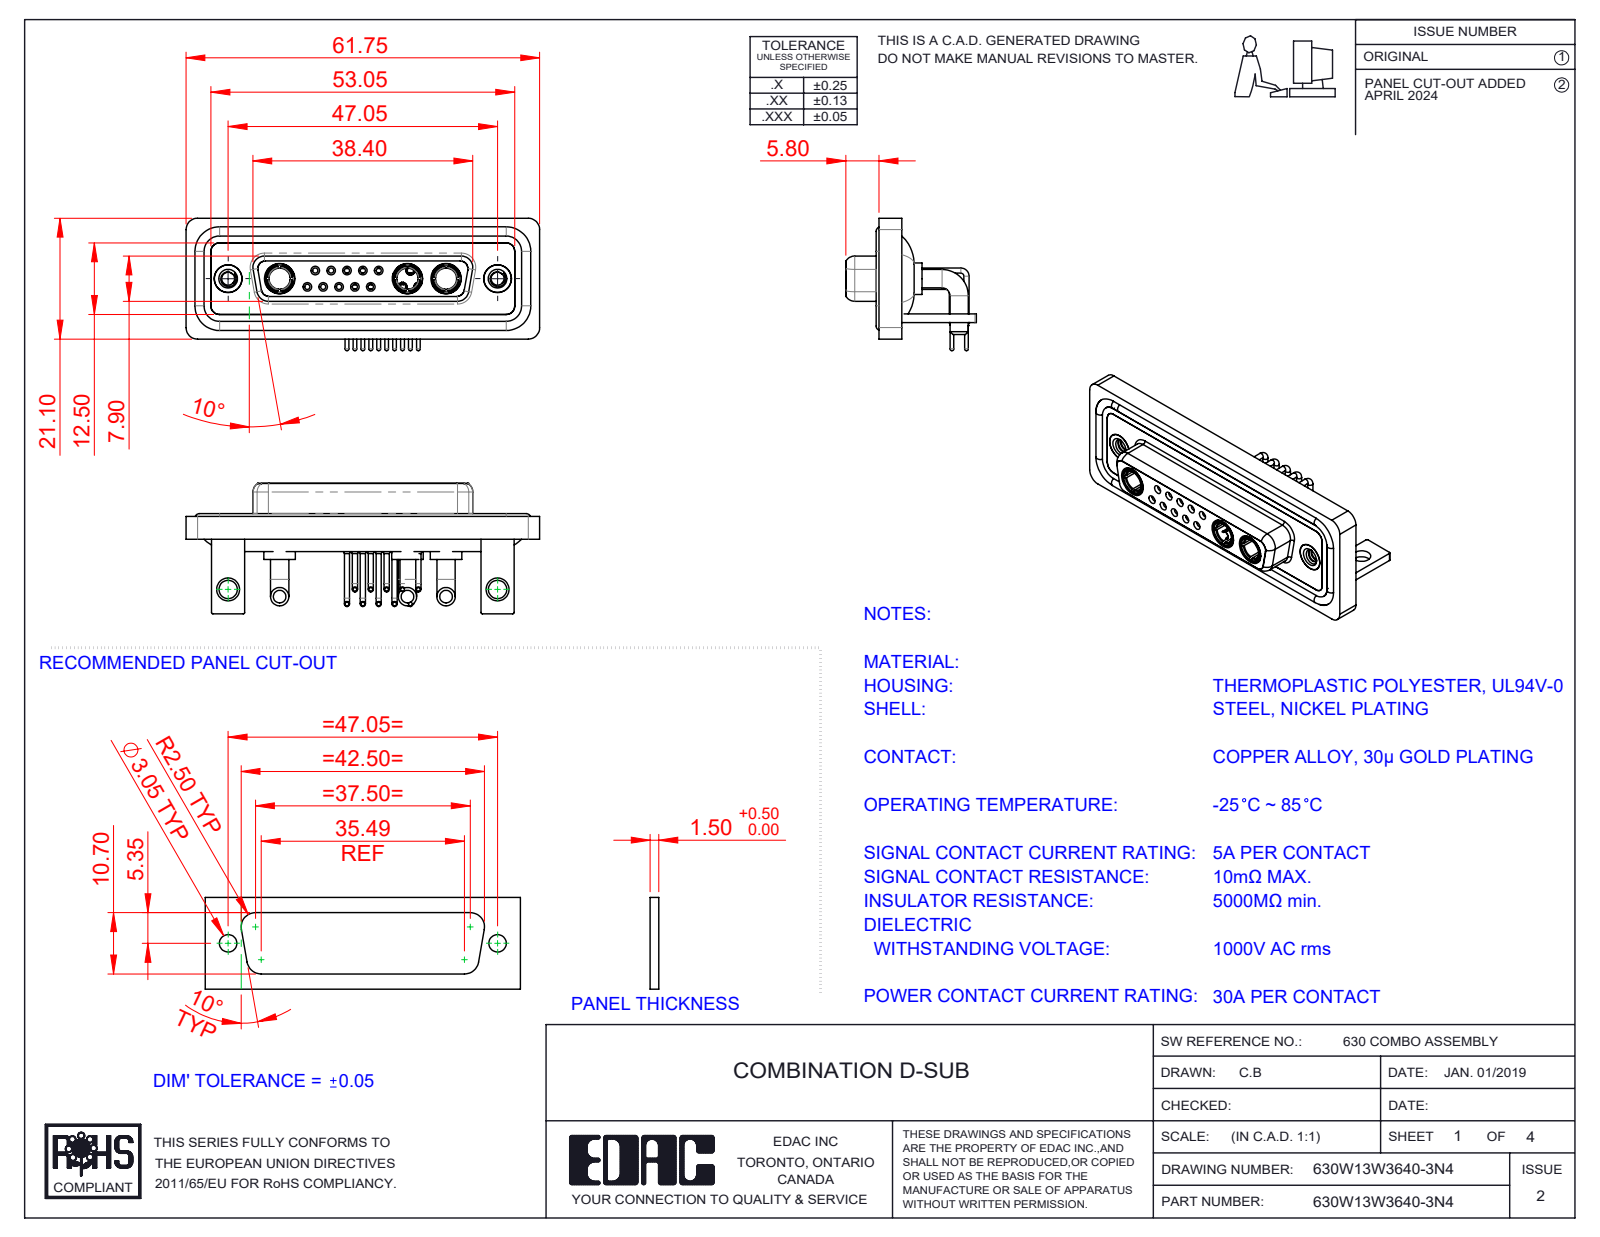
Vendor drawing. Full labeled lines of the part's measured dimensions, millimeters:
Part name (STEP PRODUCT): Power Socket_30A RA; 630Combo Threaded Rivet_2; 630Combo Stabilizer Bracket_50 Contacts; 630Combo Contact Row 1_50 Contacts (+6 more)
STEP written by: SolidWorks 2023 (CONFIG_CONTROL_DESIGN)
Units: millimetres
Bodies: 25 solids, 1198 faces (362 planar, 517 cylindrical, 319 other)
Overall size (bounding box): 61.75 × 23.12 × 22.8
Volume: 8 921 mm³ · Surface area: 15 087 mm²
Round holes (diameter × count): ⌀0.9 ×10, ⌀1.1 ×10, ⌀1.5 ×10, ⌀2 ×10, ⌀1.6 ×5, ⌀1.7 ×5, ⌀4.85 ×5, ⌀3.7 ×3, ⌀5.3 ×3, ⌀2.26 ×2, ⌀3.2 ×2, ⌀4 ×2
Round bosses / shafts (diameter × count): ⌀0.9 ×15, ⌀1.6 ×12, ⌀0.65 ×10, ⌀3.2 ×6, ⌀2 ×5, ⌀1.5 ×5, ⌀5.5 ×3, ⌀5.2 ×3
Partial cylindrical surfaces — rounded edges, fillets, slot ends (radius × count): R2 ×19, R1.5 ×18, R0.25 ×16, R1.35 ×8, R1.6 ×8, R0.5 ×5, R0.6 ×4, R0.65 ×4
Main face-to-face distances: 0.4, 1.8, 2.9, 3.7, 1.5, 4.1, 1.1, 1.4, 1.6, 3.1
Hole centre spacings: 3.16, 2.77, 5.54, 5.04, 8.31, 5.03, 7.49, 11.08
